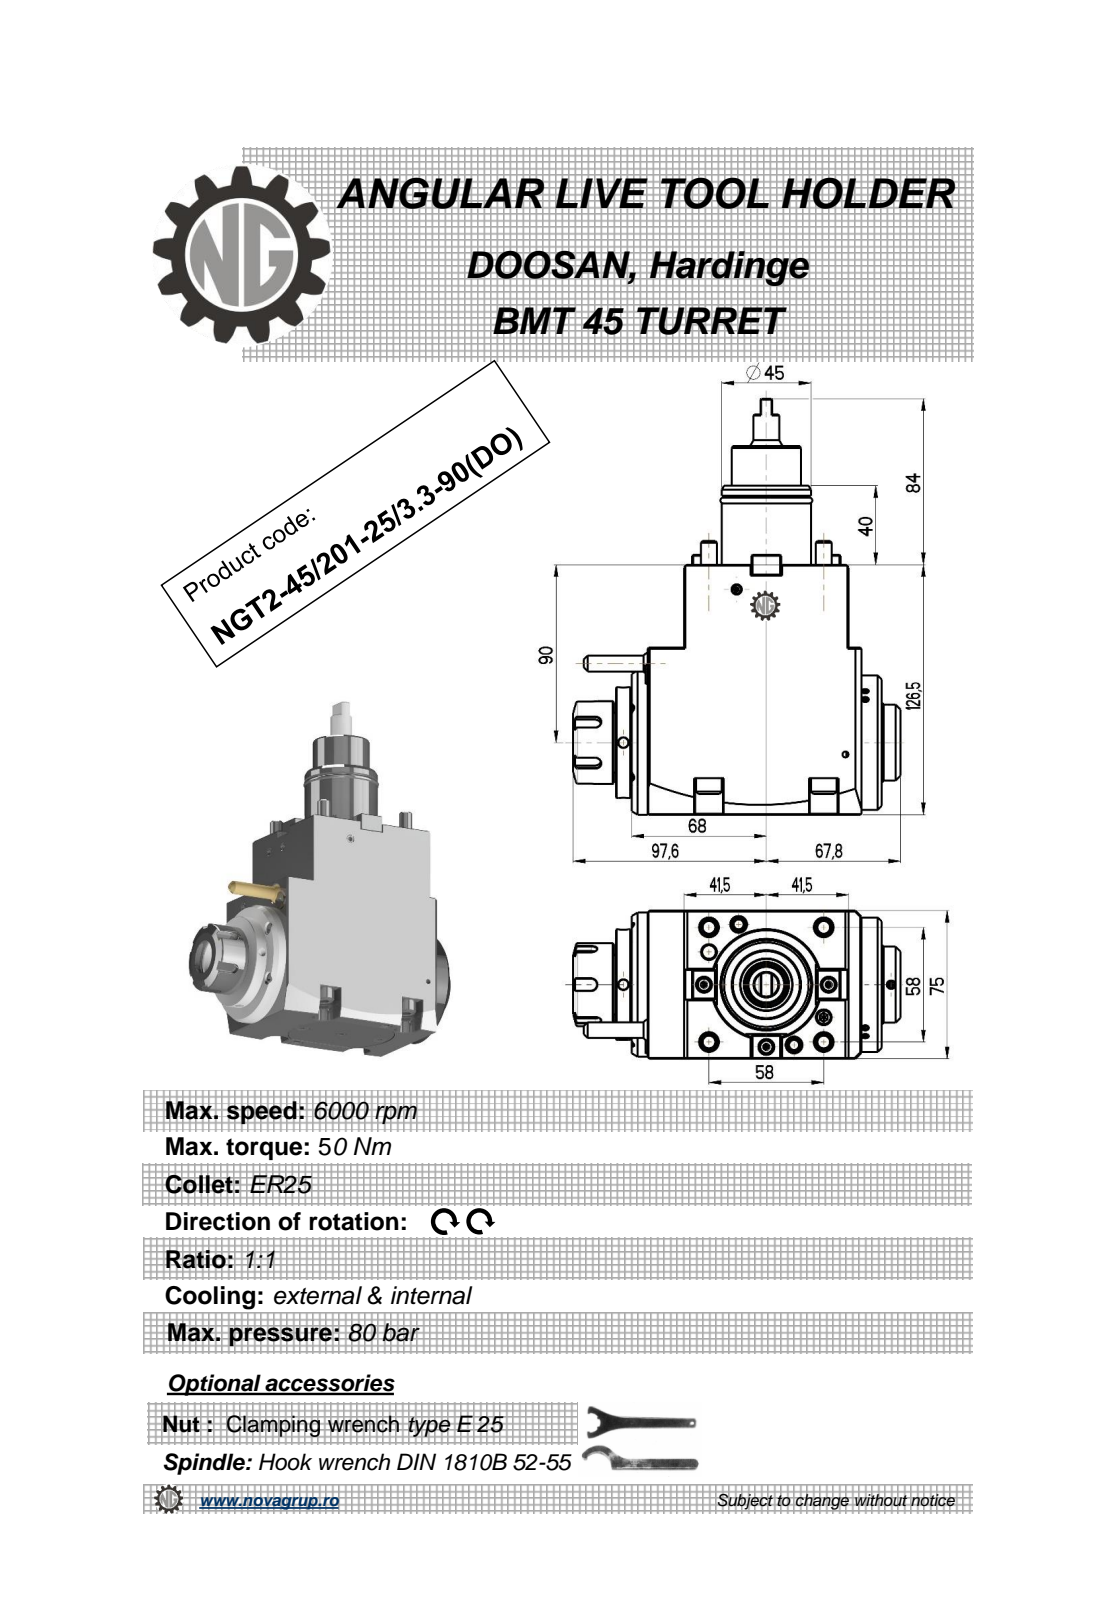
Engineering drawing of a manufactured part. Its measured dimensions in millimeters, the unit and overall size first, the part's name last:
Units: millimetres
Overall size (bounding box): 210.5 × 165.4 × 75
Round holes (diameter × count): ⌀5 ×3, ⌀6.8 ×2, ⌀3 ×1, ⌀20.3 ×1
Round bosses / shafts (diameter × count): ⌀13 ×5, ⌀8 ×5, ⌀73 ×1, ⌀68 ×1, ⌀56 ×1, ⌀45 ×1, ⌀43 ×1, ⌀42 ×1
Partial cylindrical surfaces — rounded edges, fillets, slot ends (radius × count): R0.2 ×6, R3 ×5, R7 ×4, R0.8 ×2, R550 ×2
Main face-to-face distances: 75, 8, 126.5, 83, 116, 26.5, 109.5, 89.5, 6.5, 18.5
Hole centre spacings: 46.14, 46.29, 66.73, 102.59
Volume: 1 149 000 mm³ · Surface area: 88 762 mm²
Bodies: 1 solid, 383 faces (191 planar, 85 cylindrical, 107 other)
Part name (STEP PRODUCT): NGT2_45_201_25_3_3_90_DO
STEP written by: PRO/ENGINEER BY PARAMETRIC TECHNOLOGY CORPORATION, 2010280 (CONFIG_CONTROL_DESIGN)
